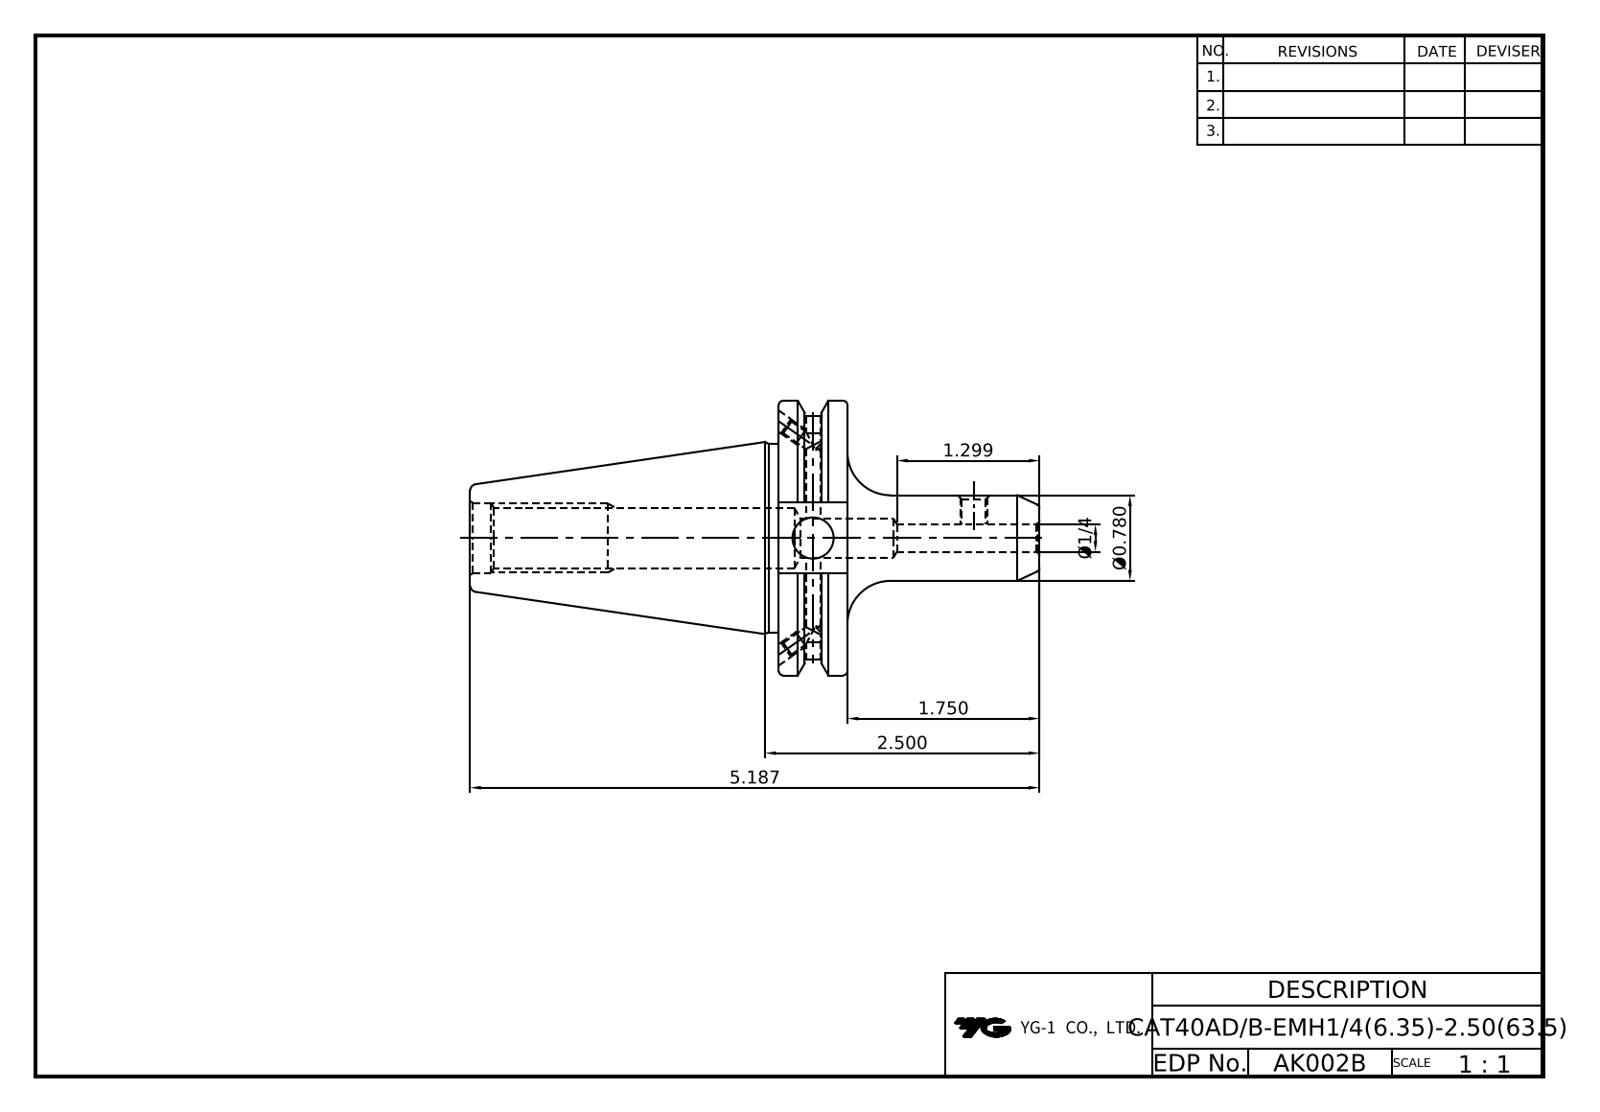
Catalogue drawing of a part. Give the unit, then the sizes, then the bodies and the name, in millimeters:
Units: millimetres
Overall size (bounding box): 131.75 × 63.5 × 61.09
Round holes (diameter × count): ⌀3.24 ×4, ⌀4 ×2, ⌀4.2 ×2, ⌀5.36 ×1, ⌀6.35 ×1, ⌀9 ×1, ⌀9.53 ×1, ⌀13.39 ×1, ⌀16.3 ×1
Round bosses / shafts (diameter × count): ⌀63.5 ×1, ⌀43.6 ×1, ⌀19.81 ×1
Partial cylindrical surfaces — rounded edges, fillets, slot ends (radius × count): R28.15 ×1
Main face-to-face distances: 15.88, 47.6, 16.38, 71.42, 87.3, 77.47, 6.05, 9.83, 81.3, 9.88
Volume: 113 812 mm³ · Surface area: 24 388 mm²
Bodies: 1 solid, 87 faces (35 planar, 28 cylindrical, 24 other)
Part name (STEP PRODUCT): LO-CAT40ADB-EMH6.35-63.5
STEP written by: Autodesk Inventor 2025 (AUTOMOTIVE_DESIGN)
